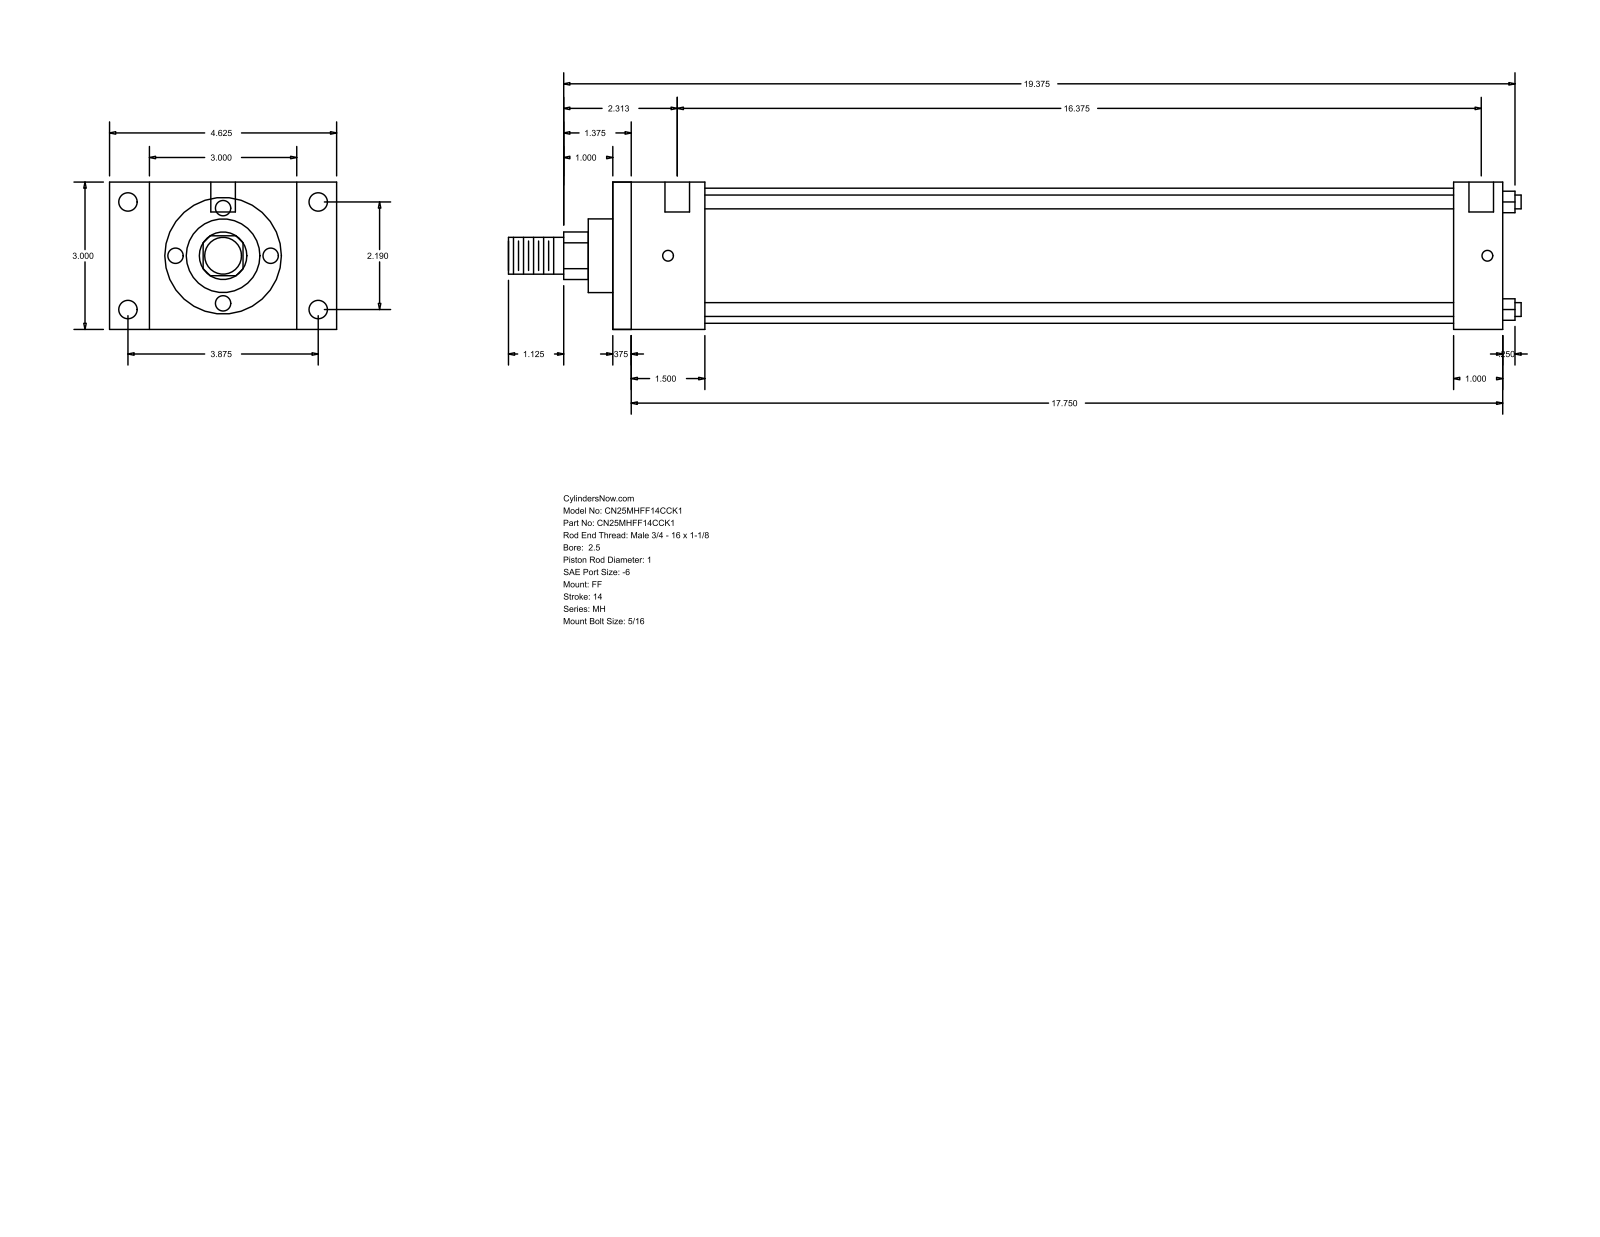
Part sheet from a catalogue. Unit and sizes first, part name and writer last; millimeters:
Units: millimetres
Overall size (bounding box): 523.88 × 117.47 × 76.2
Round holes (diameter × count): ⌀5.56 ×4, ⌀9.53 ×4, ⌀12.7 ×2
Round bosses / shafts (diameter × count): ⌀7.14 ×4, ⌀69.85 ×1, ⌀38.1 ×1, ⌀25.4 ×1, ⌀19.05 ×1
Partial cylindrical surfaces — rounded edges, fillets, slot ends (radius × count): R12.29 ×1
Main face-to-face distances: 76.2, 460.37, 450.85, 9.52, 25.39, 47.63, 434.98, 38.11, 425.46, 387.35
Hole centre spacings: 55.62, 98.42, 113.05, 423.86, 3.18, 4.76, 415.92, 419.1
Bodies: 0 solids, 92 faces (64 planar, 28 cylindrical, 0 other)
Part name (STEP PRODUCT): MH_FF__0250_1
STEP written by: GSSL Pune (CONFIG_CONTROL_DESIGN)
